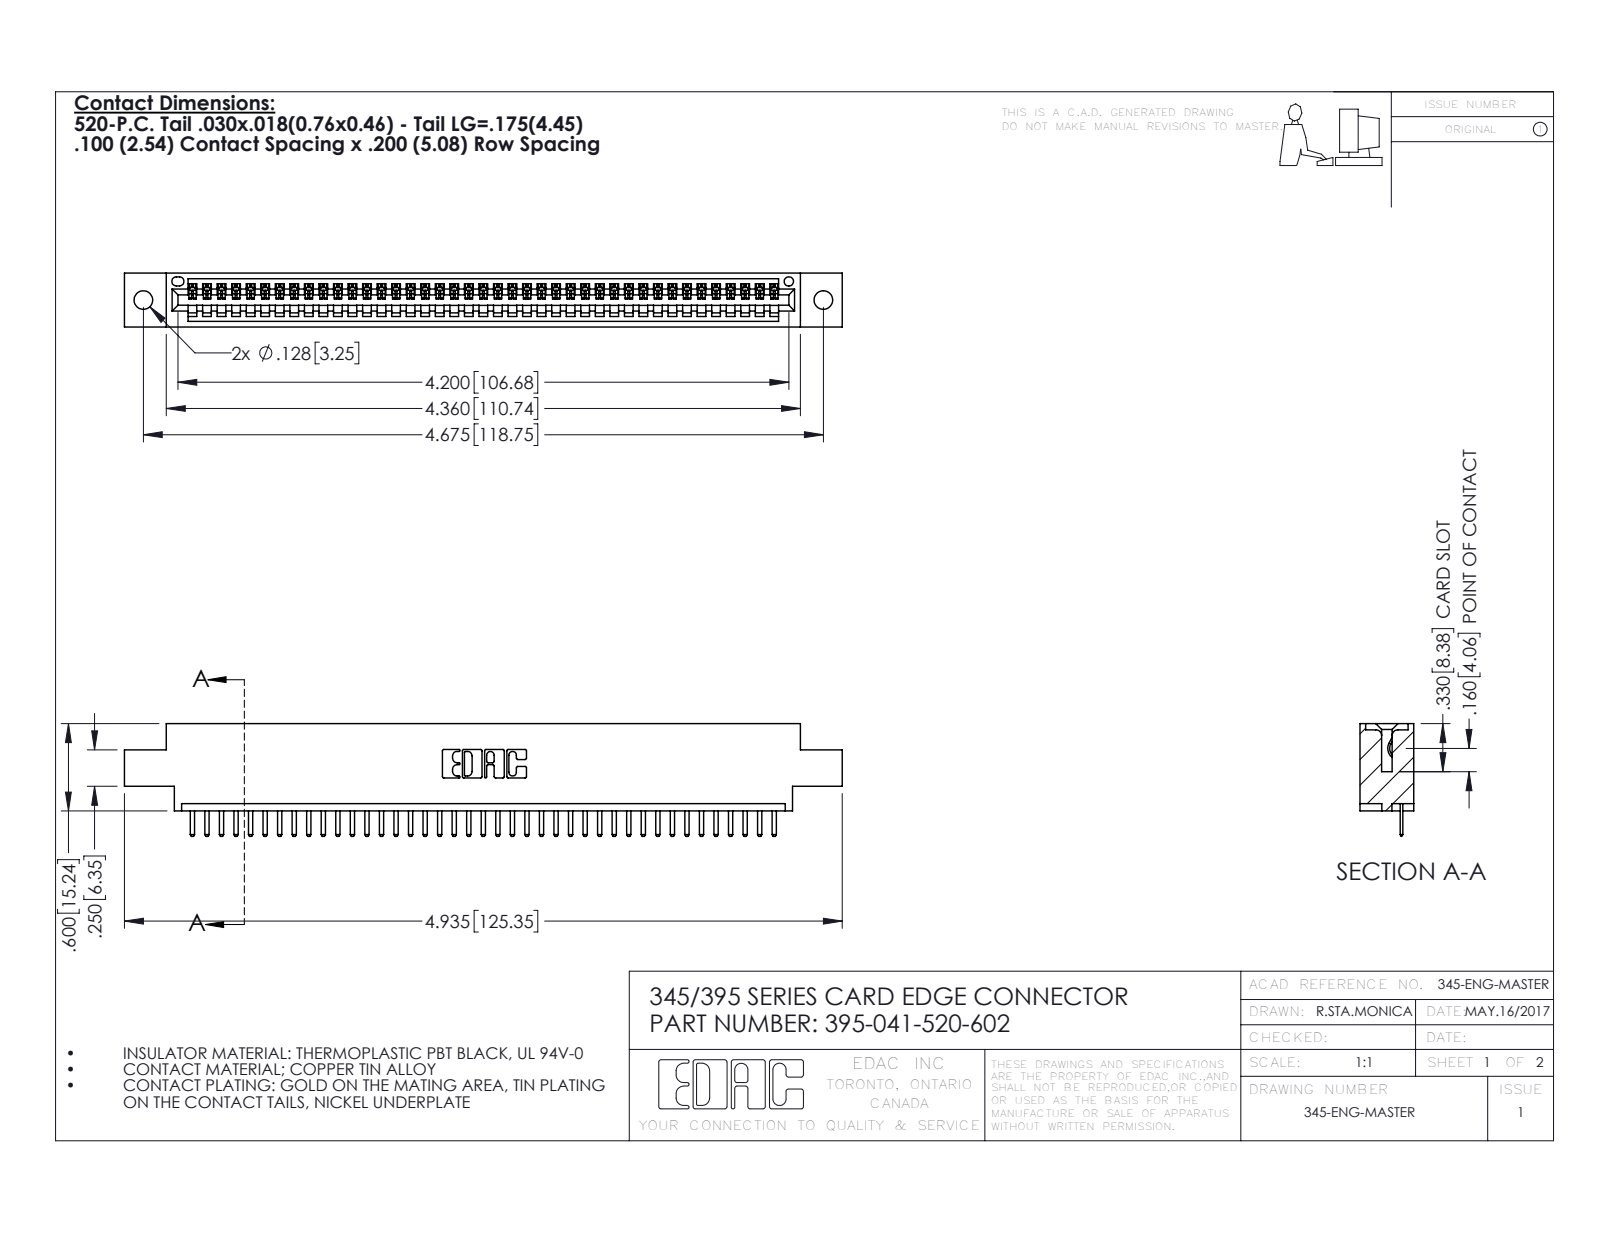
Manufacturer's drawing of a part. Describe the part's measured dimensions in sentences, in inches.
The part is named "395-041-520-602; 345-292-001_345-293-120; 345 Part_0.170 Offset - 0.128 Dia". Its 3-D file was written by "SolidWorks 2016 (CONFIG_CONTROL_DESIGN)". It is 42 solids with 2672 faces: 1806 planar, 866 cylindrical and 0 other. Overall it measures 4.935 by 0.775 by 0.37 inches. Its volume is 0.71 cubic inches and its surface area 23.11 square inches. Round holes: 2 of diameter 0.128, 1 of diameter 0.064. Partial cylindrical surfaces (rounded edges, fillets, slot ends): 84 of radius 0.01, 82 of radius 0.006, 22 of radius 0.01, 6 of radius 0.007, 6 of radius 0.031, 3 of radius 0.026, 2 of radius 0.031, 2 of radius 0.04. The main face-to-face distances are 0.298, 0.072, 0.37, 0.2, 0.098, 0.272, 0.025, 0.225, 0.072, 0.175. The hole center spacings are 0.27, 4.439, 4.675.
